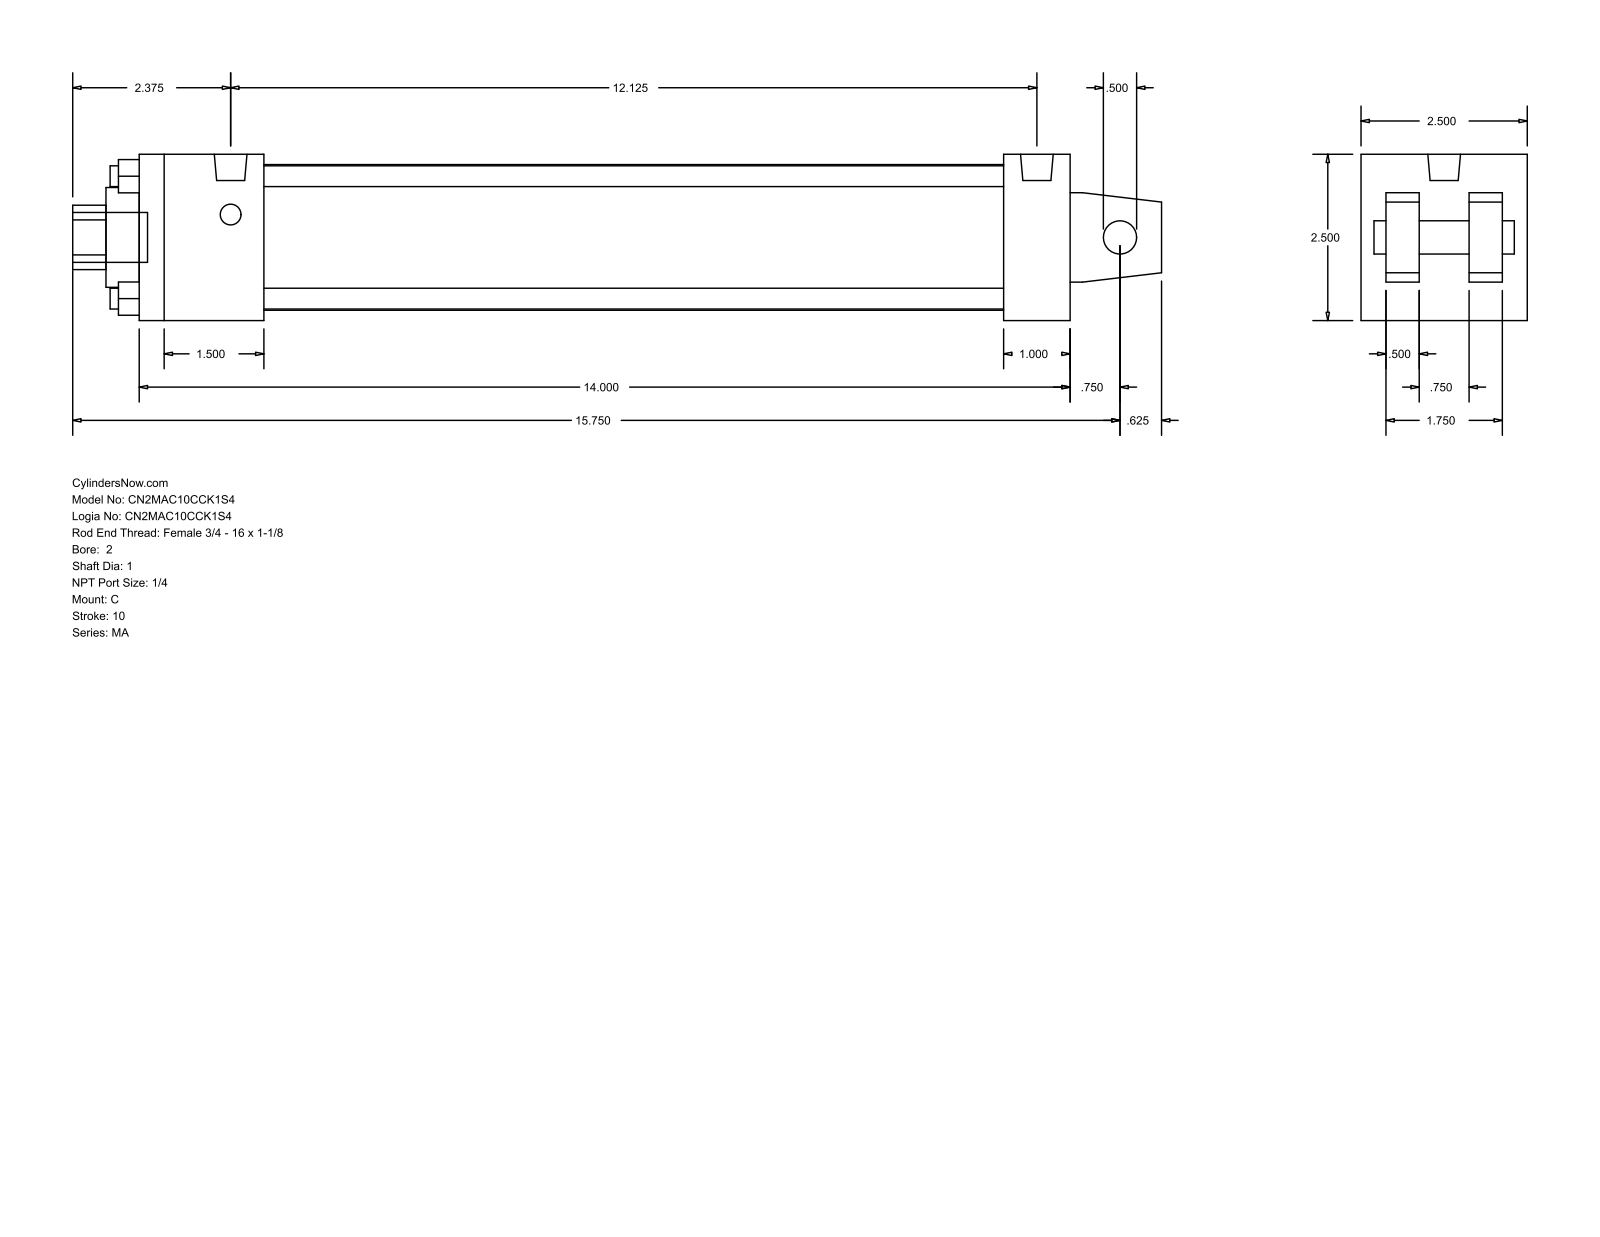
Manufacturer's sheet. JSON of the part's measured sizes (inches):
{"part_name": "MA_C__0200_1", "step_written_by": "GSSL Pune (CONFIG_CONTROL_DESIGN)", "units": "inches", "bodies": {"solids": 0, "faces": 103, "planar": 76, "cylindrical": 27, "other": 0}, "overall_size": [16.375, 2.5, 2.5], "round_holes": [[0.313, 4], [0.5, 1], [1, 1], [1.5, 1], [2.19, 1]], "round_bosses_or_shafts": [[0.313, 4], [0.492, 2], [0.75, 1]], "partial_cylinders_radius": [[0.484, 1]], "face_to_face_distances": [2.5, 0.5, 14, 0.875, 1.625, 0.375, 2.125, 1.25, 1.875, 1], "hole_center_spacings": [1.301, 1.84, 2.602]}
